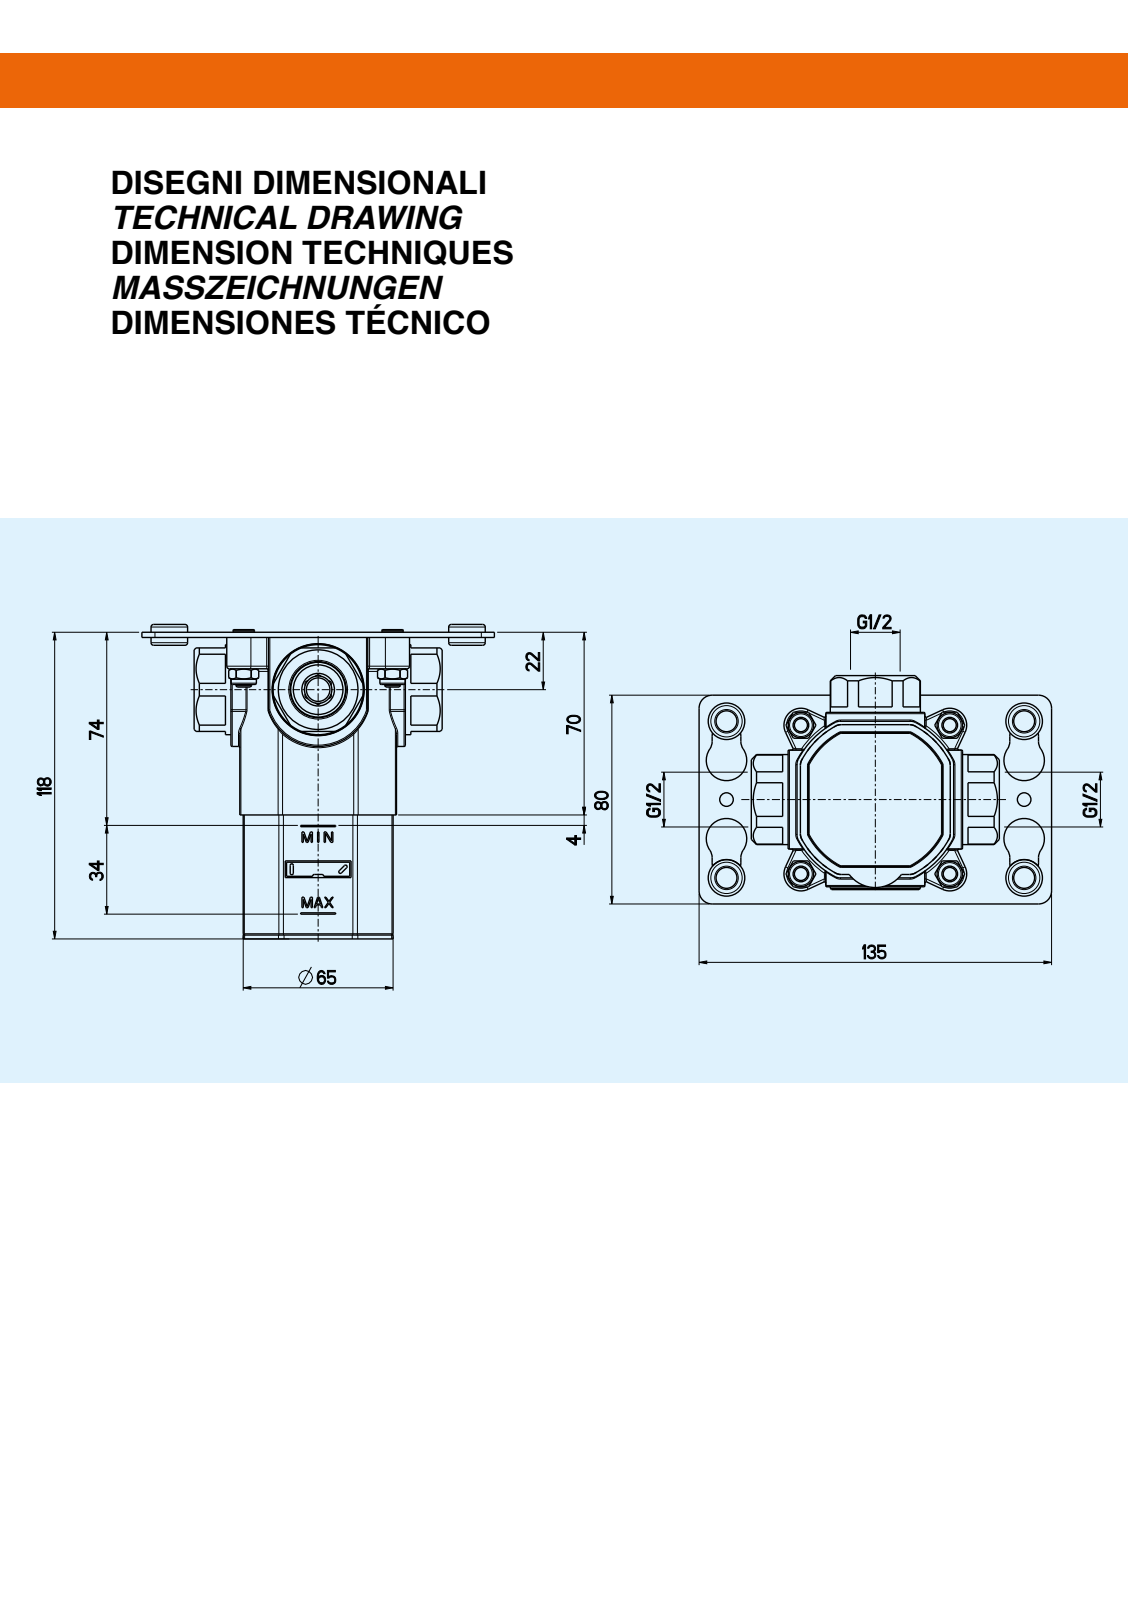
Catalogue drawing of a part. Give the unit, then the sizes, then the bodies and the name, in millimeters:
Units: millimetres
Overall size (bounding box): 81 × 76.2 × 72
Round holes (diameter × count): ⌀2.5 ×2, ⌀3.2 ×1, ⌀30 ×1, ⌀35.7 ×1, ⌀36 ×1, ⌀37.4 ×1, ⌀37.6 ×1, ⌀40 ×1, ⌀41 ×1, ⌀44.8 ×1, ⌀69.5 ×1
Round bosses / shafts (diameter × count): ⌀72 ×1, ⌀50 ×1, ⌀38 ×1, ⌀37.3 ×1, ⌀34.5 ×1
Partial cylindrical surfaces — rounded edges, fillets, slot ends (radius × count): R0.1 ×12, R0.4 ×4, R0.56 ×2, R0.73 ×2, R2 ×2, R2.3 ×2, R8 ×2, R0.49 ×1
Main face-to-face distances: 2.3, 51.7, 54, 47.1, 4.6, 49.4, 5, 2.7, 56.7, 52.1
Hole centre spacings: 12, 13.5, 25.5
Volume: 33 806 mm³ · Surface area: 33 315 mm²
Bodies: 5 solids, 266 faces (126 planar, 57 cylindrical, 83 other)
Part name (STEP PRODUCT): AF031EXT-00; ABIX604C001_AF0; SCCBSC0002; AF031-001_oa_0 (+3 more)
STEP written by: Solid Edge (AUTOMOTIVE_DESIGN)
